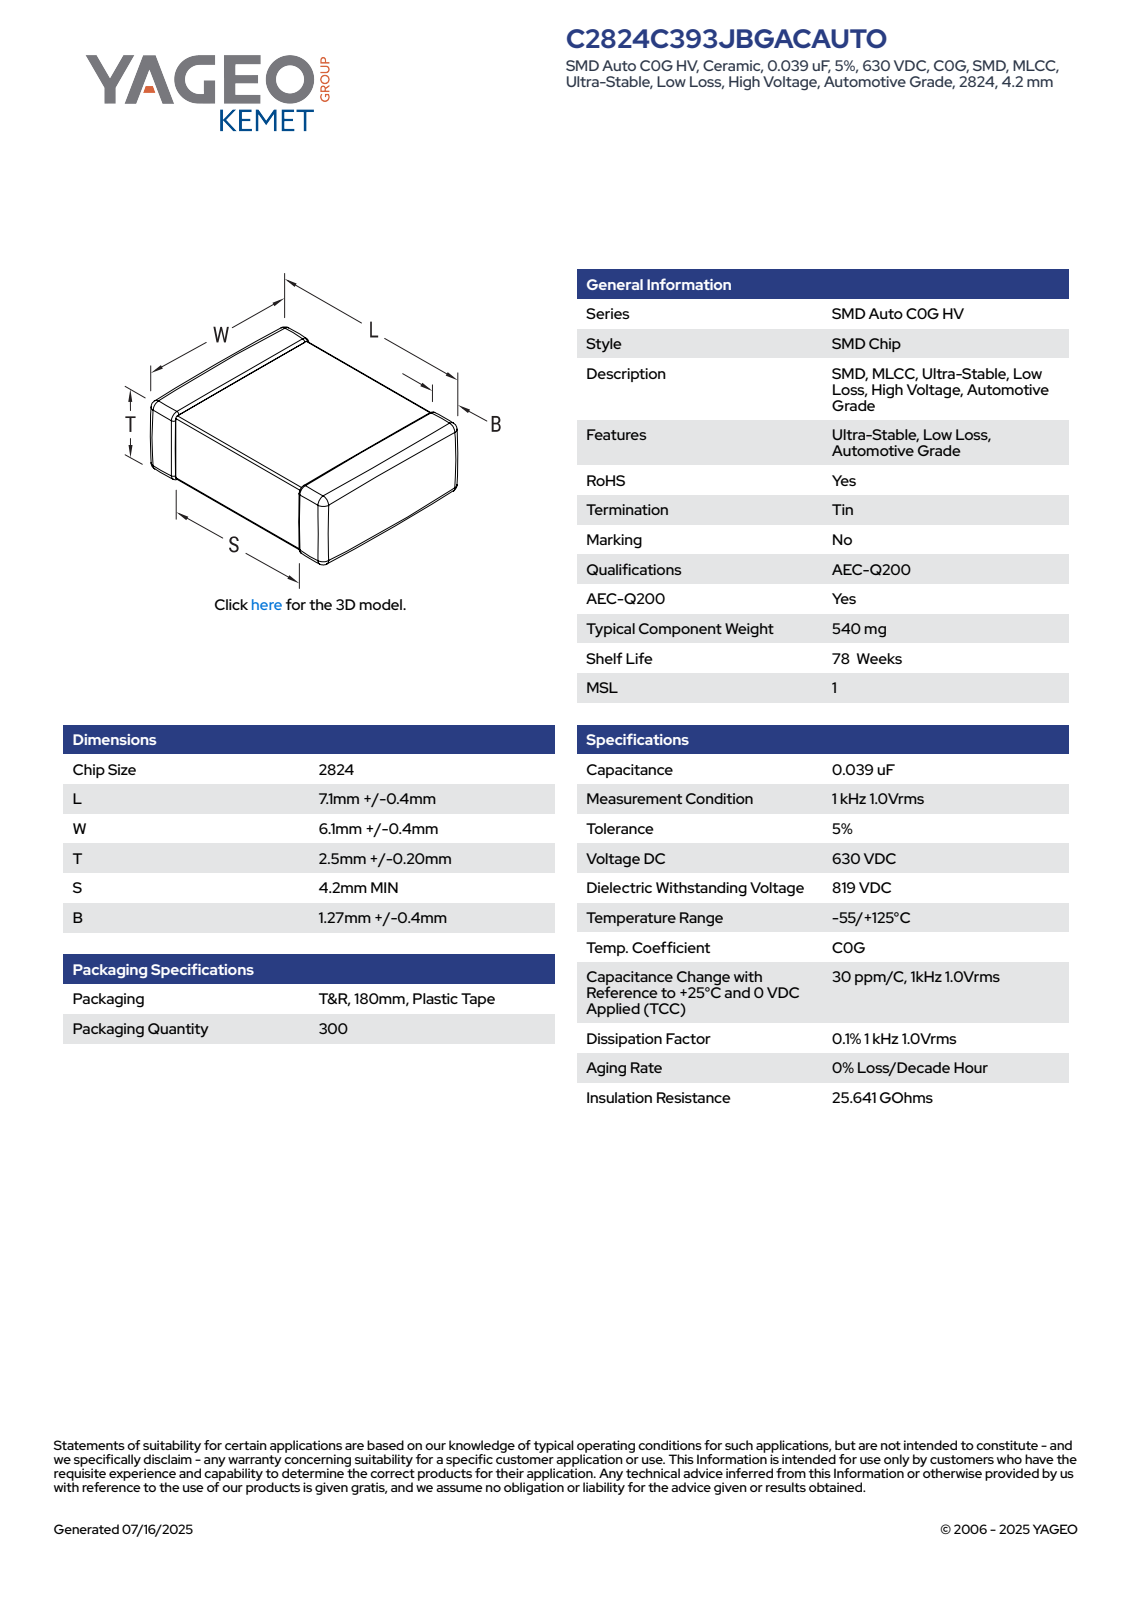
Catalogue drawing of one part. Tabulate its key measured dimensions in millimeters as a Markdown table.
| quantity | value |
| --- | --- |
| part name | CCS_CCSTDNOS_2824_L7.5W6.5T2.7B1.67 |
| STEP written by | SolidWorks 2014 (AUTOMOTIVE_DESIGN) |
| units | millimeters |
| bodies | 4 solids, 121 faces (71 planar, 34 cylindrical, 16 other) |
| overall size | 7.5 × 6.5 × 2.7 |
| volume | 121 mm³ |
| surface area | 169 mm² |
| partial cylindrical surfaces (radius × count) | 0.14 × 24 |
| main face-to-face distances | 2.56, 2.42, 2.7, 7.5, 6.36, 6.22, 6.5, 2.57, 2.43, 0.53 |
